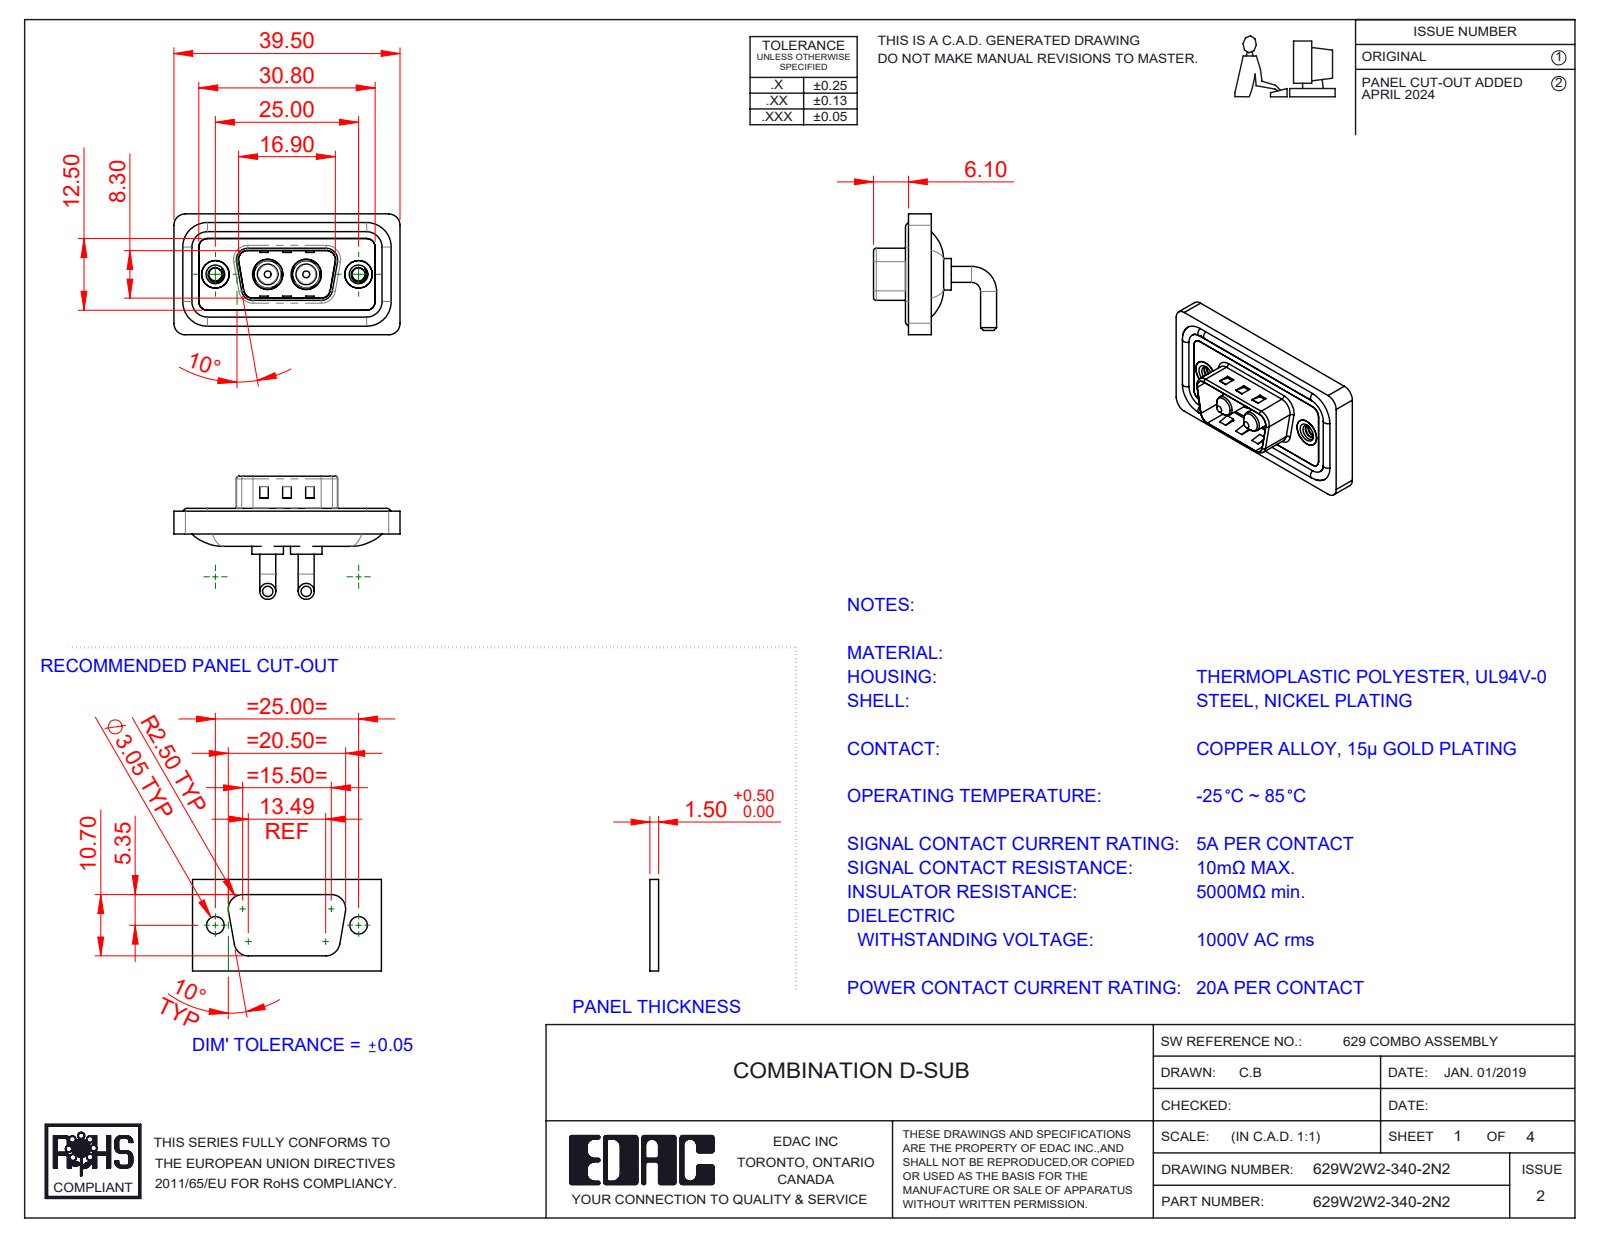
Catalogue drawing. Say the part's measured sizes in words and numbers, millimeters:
The part is named "629Combo Housing_2W2; 629Combo Waterproof Housing_09 Contacts; 629Combo Shell Rear_09 Contacts; Power Pin_20A RA (+3 more)". Its 3-D file was written by "SolidWorks 2023 (CONFIG_CONTROL_DESIGN)". It is 11 solids with 497 faces: 165 planar, 222 cylindrical and 110 other. Overall it measures 39.5 by 21.5 by 21.1 millimeters. Its volume is 4 595 cubic millimeters and its surface area 7 168 square millimeters. Round holes: 2 of diameter 2.26, 2 of diameter 4, 2 of diameter 4.8, 2 of diameter 4.85, 2 of diameter 5, 2 of diameter 5.3. Round bosses or shafts: 4 of diameter 2.8, 4 of diameter 1.6, 2 of diameter 5.5, 2 of diameter 5.2, 2 of diameter 4.9, 2 of diameter 4.75, 2 of diameter 3.75, 2 of diameter 3.6. Partial cylindrical surfaces (rounded edges, fillets, slot ends): 18 of radius 1.5, 18 of radius 2, 8 of radius 0.5, 8 of radius 1.6, 4 of radius 0.25, 4 of radius 0.6, 4 of radius 0.65, 4 of radius 0.9. The main face-to-face distances are 0.4, 2.9, 1.1, 0.8, 2.1, 2.5, 3.1, 1.6, 4.5, 1.5. The hole center spacings are 9.14, 15.86, 6.72, 25.
